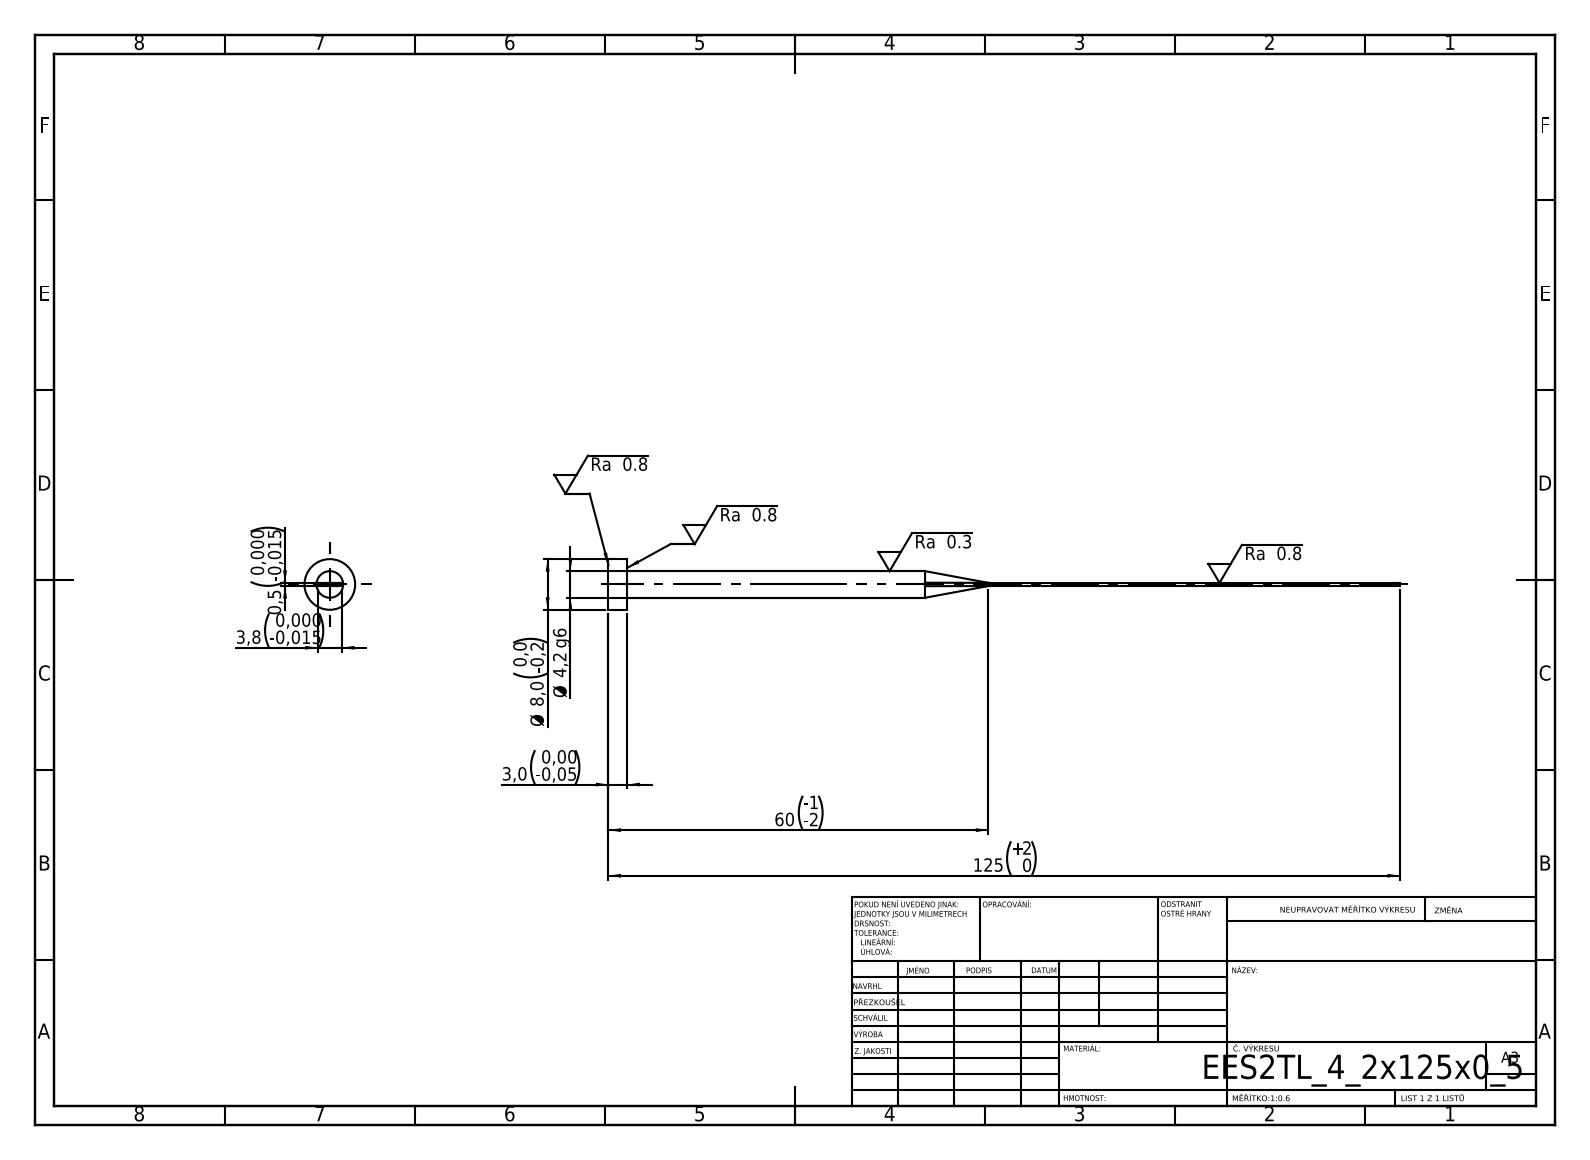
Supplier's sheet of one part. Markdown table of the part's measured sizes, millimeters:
| quantity | value |
| --- | --- |
| STEP written by | SolidWorks 2019 (CONFIG_CONTROL_DESIGN) |
| units | millimeters |
| bodies | 1 solid, 15 faces (7 planar, 4 cylindrical, 4 other) |
| overall size | 125 × 8 × 8 |
| volume | 999 mm³ |
| surface area | 1 447 mm² |
| round bosses / shafts (diameter × count) | 8 × 1, 4.2 × 1 |
| main face-to-face distances | 0.5, 3, 3.8, 125, 122 |
